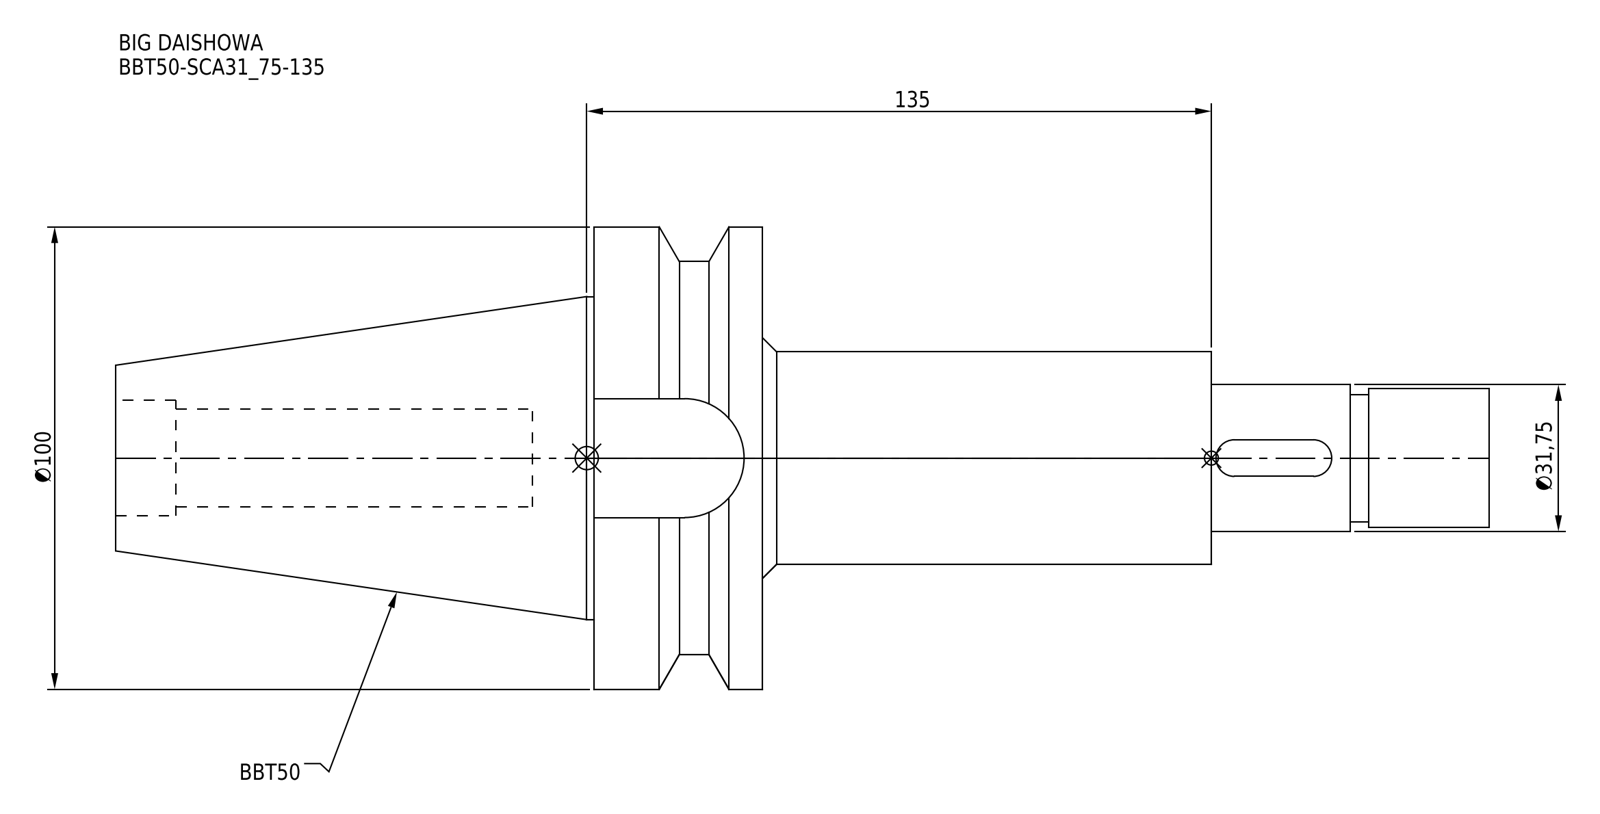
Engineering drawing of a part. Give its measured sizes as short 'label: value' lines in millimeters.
name: BBT50-SCA31_75-135
written by: CREO PARAMETRIC BY PTC INC, 2016380 (AUTOMOTIVE_DESIGN)
unit: mm
bodies: 1 solid, 42 faces (12 planar, 22 cylindrical, 8 other)
size: 296.8 × 100 × 100
volume: 689 913 mm³; area: 70 859 mm²
holes: 1× ⌀21.2, 1× ⌀25
bosses: 1× ⌀100, 1× ⌀85, 1× ⌀69.85, 1× ⌀46, 1× ⌀31.75, 1× ⌀30, 1× ⌀27.5
rounds: 2× R3.96
face distances: 36.5, 97, 133.5, 236.8, 139.8, 103.3, 60, 157, 193.5, 296.8
